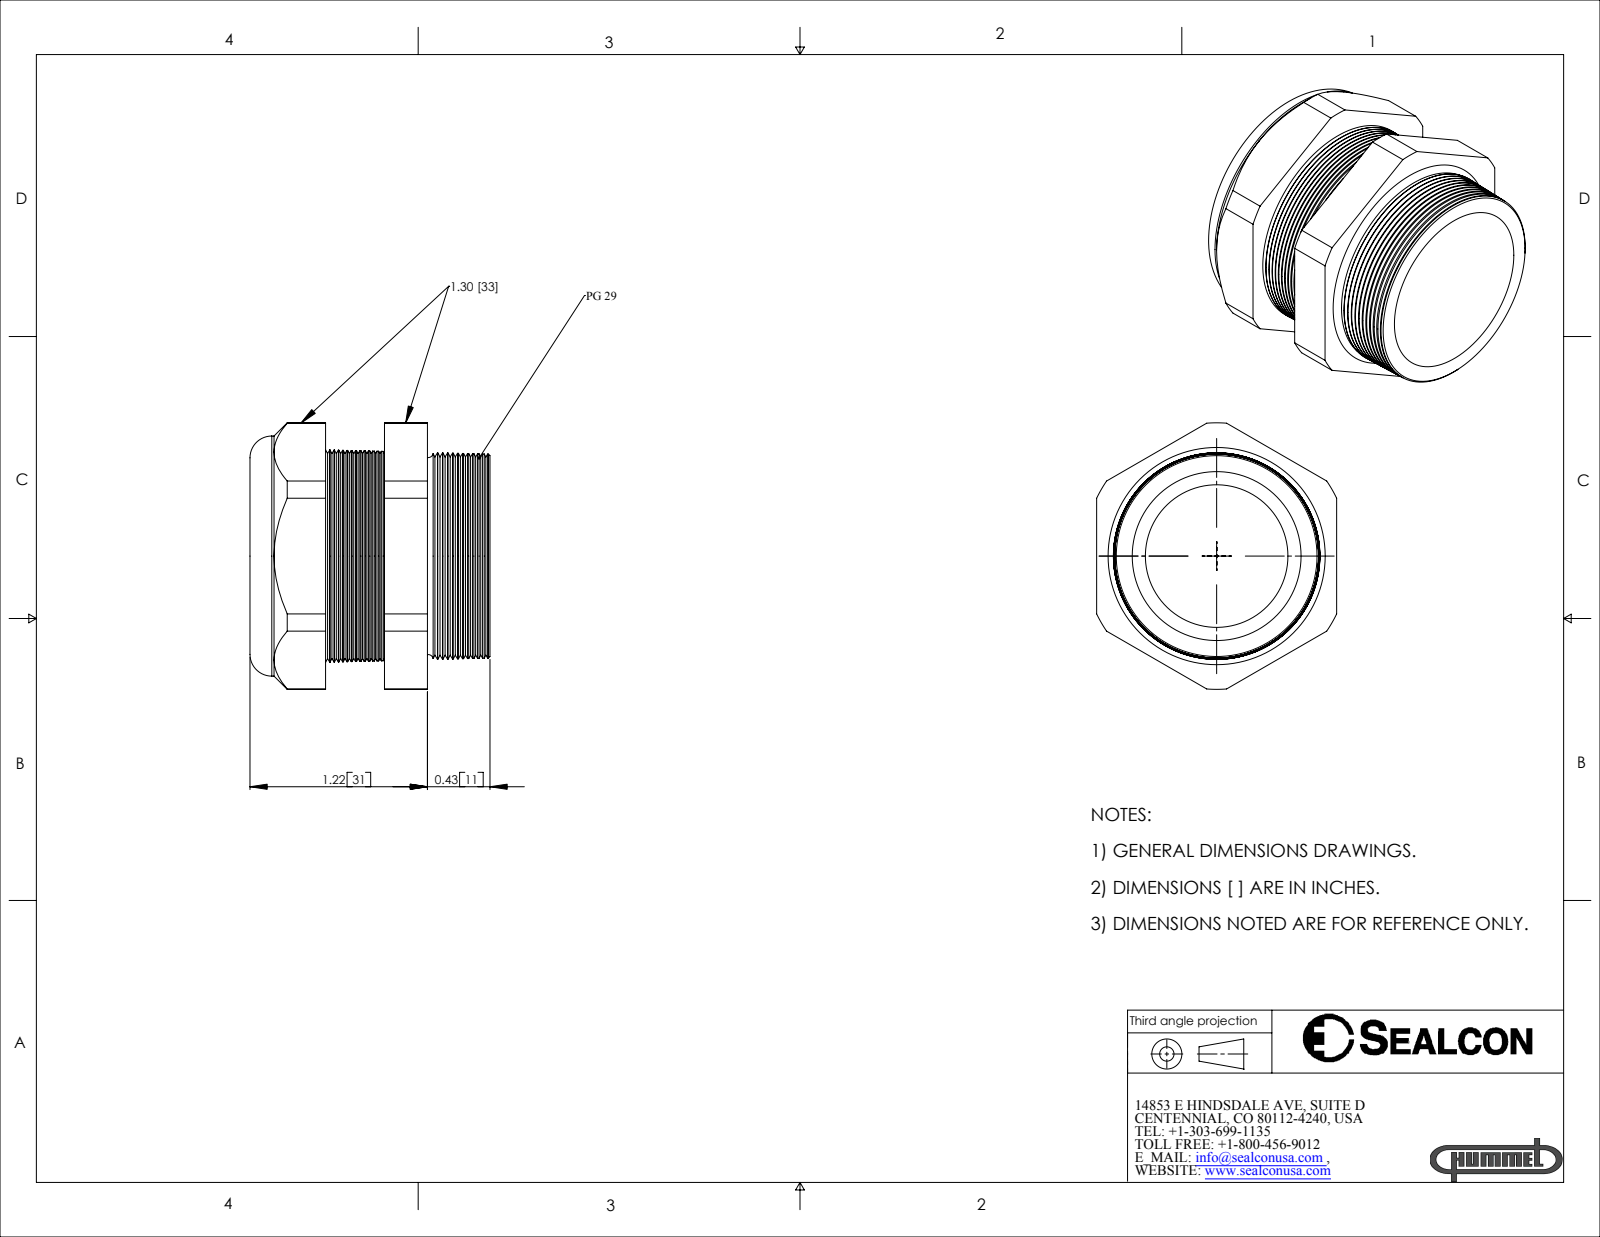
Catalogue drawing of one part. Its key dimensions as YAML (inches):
part_name: "CD29AP-BK"
step_written_by: "SolidWorks 2007 (CONFIG_CONTROL_DESIGN)"
units: inches
bodies: {solids: 2, faces: 206, planar: 20, cylindrical: 20, other: 166}
overall_size: [1.831, 1.65, 1.65]
volume: 2.093
surface_area: 23.65
round_holes:
  - {diameter: 0.96, count: 1}
  - {diameter: 0.98, count: 1}
round_bosses_or_shafts:
  - {diameter: 1.65, count: 1}
partial_cylinders:
  - {radius: 0.916, count: 1}
face_to_face_distances: [1.65, 0.48, 0.02, 0.5, 0.925, 0.905, 0.425, 0.52, 0.5, 0.02]
